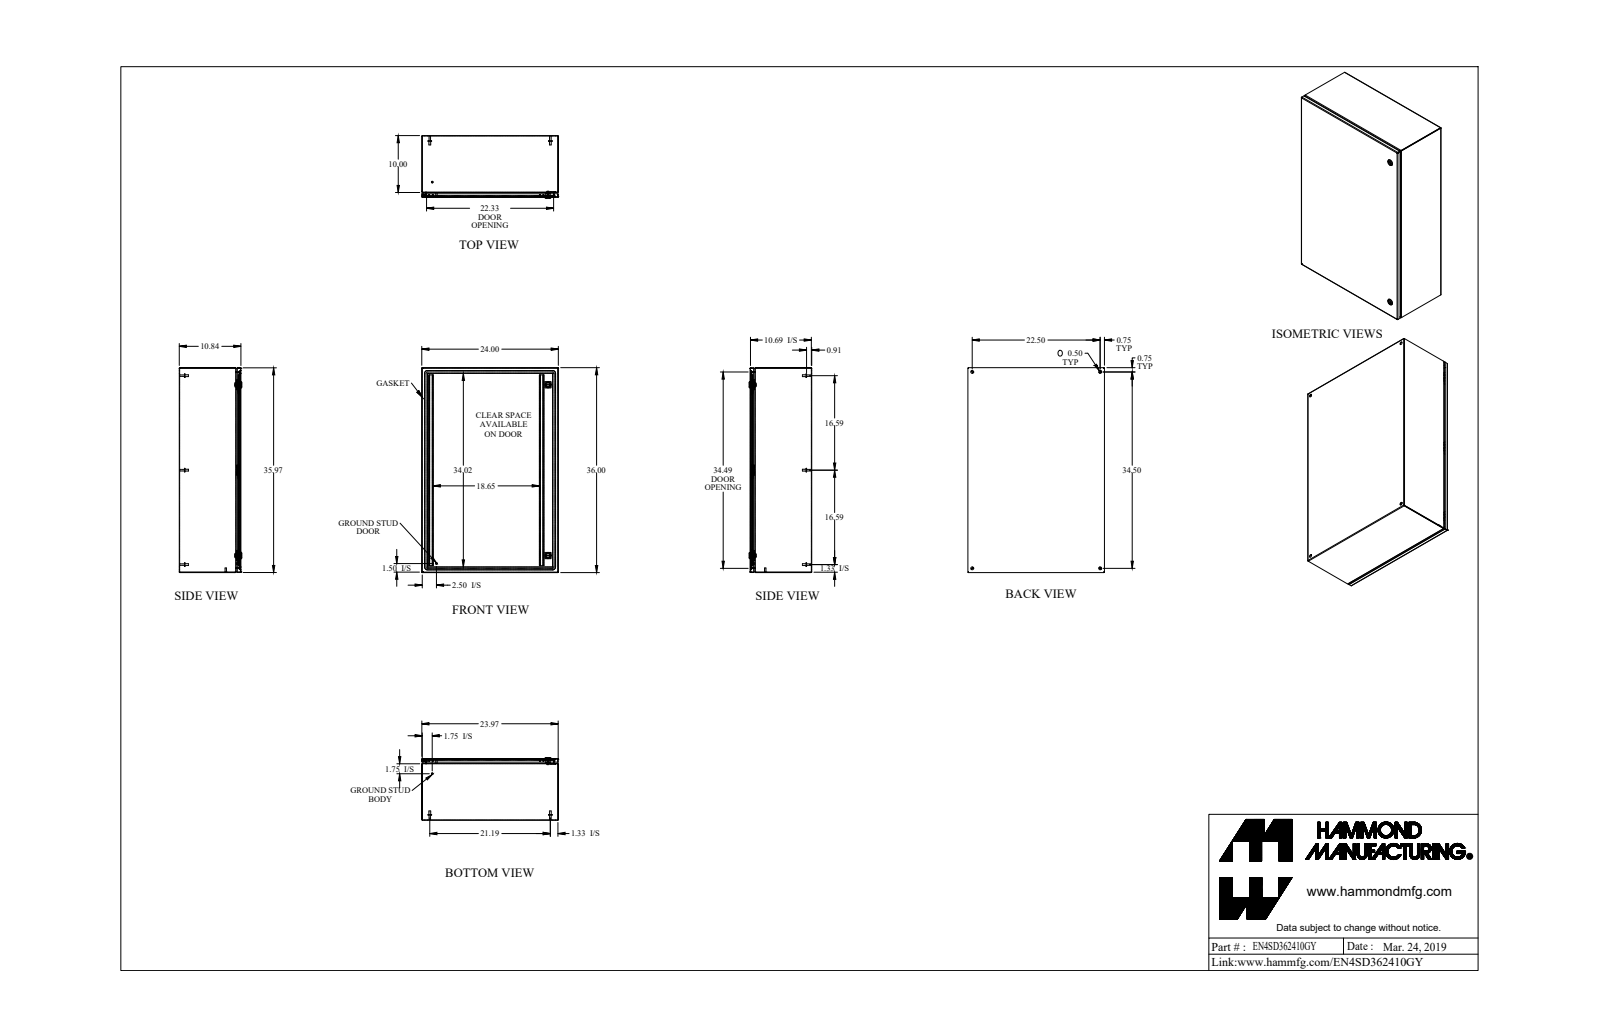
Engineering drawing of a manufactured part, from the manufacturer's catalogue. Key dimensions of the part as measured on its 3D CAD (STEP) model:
Part name (STEP PRODUCT): EN4SD362410GY
STEP written by: SolidWorks 2019 (AUTOMOTIVE_DESIGN)
Units: inches
Bodies: 33 solids, 917 faces (430 planar, 307 cylindrical, 180 other)
Overall size (bounding box): 36 × 24 × 10.997
Volume: 244.1 in³ · Surface area: 6 852 in²
Round holes (diameter × count): ⌀0.5 ×4, ⌀0.232 ×2, ⌀0.625 ×2, ⌀0.785 ×2, ⌀0.172 ×1, ⌀0.24 ×1, ⌀0.242 ×1
Round bosses / shafts (diameter × count): ⌀0.625 ×6, ⌀0.313 ×6, ⌀0.27 ×6, ⌀1.1 ×2, ⌀0.525 ×2, ⌀0.281 ×2, ⌀0.25 ×2, ⌀0.455 ×1
Partial cylindrical surfaces — rounded edges, fillets, slot ends (radius × count): R0.036 ×20, R0.108 ×20, R0.043 ×12, R0.081 ×12, R0.382 ×12, R19.003 ×8, R0.006 ×6, R0.062 ×6
Main face-to-face distances: 0.072, 10.765, 10.693, 10.837, 23.928, 35.928, 23.856, 24, 35.856, 36
Hole centre spacings: 22.5, 34.5, 41.189, 2.493, 2.494, 21.544, 21.545, 29.999
